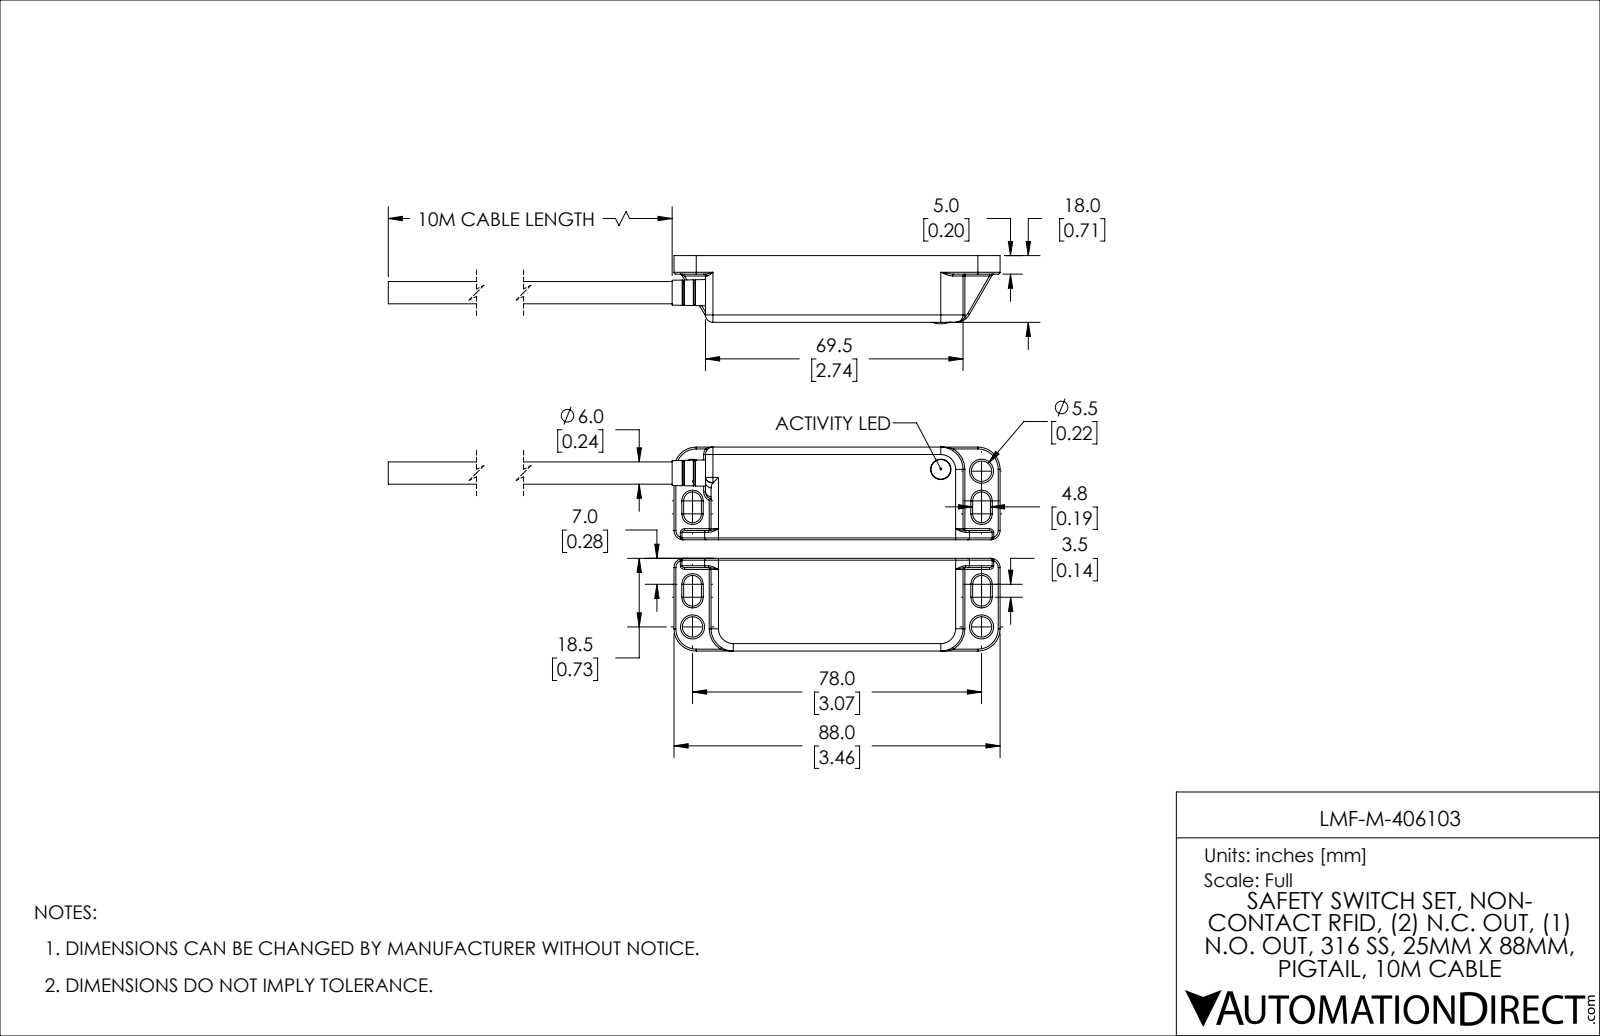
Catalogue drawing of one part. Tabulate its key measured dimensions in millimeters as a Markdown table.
| quantity | value |
| --- | --- |
| part name | 406-LMF |
| STEP written by | SolidWorks 2019 (AUTOMOTIVE_DESIGN) |
| units | millimeters |
| bodies | 13 solids, 1351 faces (580 planar, 335 cylindrical, 436 other) |
| overall size | 152.5 × 55 × 18.4 |
| volume | 31 770 mm³ |
| surface area | 32 760 mm² |
| round holes (diameter × count) | 5.5 × 5, 7.2 × 5, 3.5 × 4, 6 × 2, 6.1 × 2, 2.9 × 1, 4.5 × 1, 5.9 × 1 |
| round bosses / shafts (diameter × count) | 7 × 4, 6 × 3, 3.2 × 2, 8.6 × 1, 7.6 × 1, 7.1 × 1, 6.4 × 1, 5.3 × 1 |
| partial cylindrical surfaces (radius × count) | 0.5 × 118, 0.3 × 32, 2 × 10, 6 × 9, 2.4 × 8, 4 × 6, 0.2 × 4, 2.5 × 4 |
| main face-to-face distances | 2, 30, 23, 15.7, 1.5, 17.7, 25, 5, 14.2, 16.2 |
| hole center spacings | 15, 15.8, 29.4, 37.4, 39.3, 42, 50, 58 |
